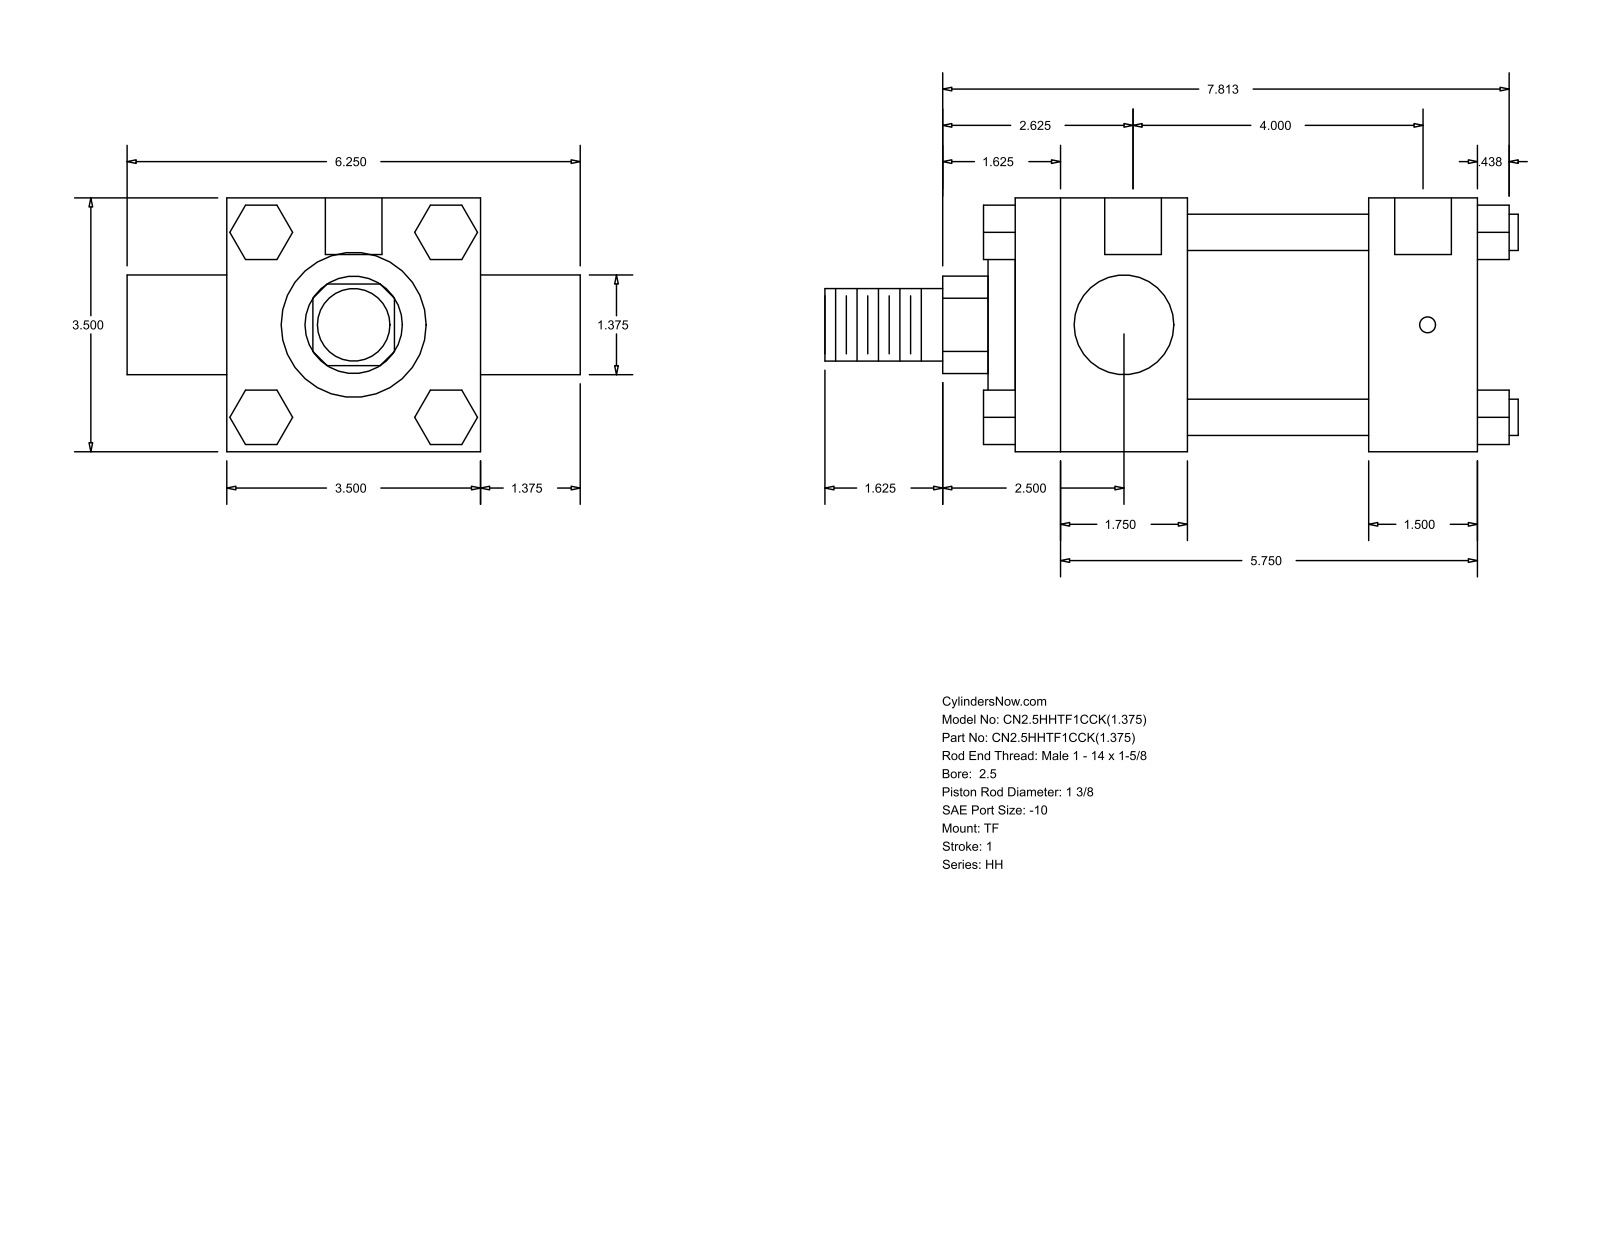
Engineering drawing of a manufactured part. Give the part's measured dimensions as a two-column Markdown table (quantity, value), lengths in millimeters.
| quantity | value |
| --- | --- |
| part name | HH_TF__0250_1.375 |
| STEP written by | GSSL Pune (CONFIG_CONTROL_DESIGN) |
| units | millimeters |
| bodies | 0 solids, 120 faces (92 planar, 28 cylindrical, 0 other) |
| overall size | 242.89 × 158.75 × 88.9 |
| round holes (diameter × count) | 5.56 × 3, 19.84 × 2 |
| round bosses / shafts (diameter × count) | 12.7 × 4, 34.92 × 2, 73.03 × 1, 50.8 × 1, 25.4 × 1 |
| partial cylindrical surfaces (radius × count) | 17.06 × 1 |
| main face-to-face distances | 88.9, 161.92, 60.32, 101.6, 123.82, 63.5, 38.1, 19.05, 32.38, 56.09 |
| hole center spacings | 1.58, 103.19, 101.61, 104.77 |
